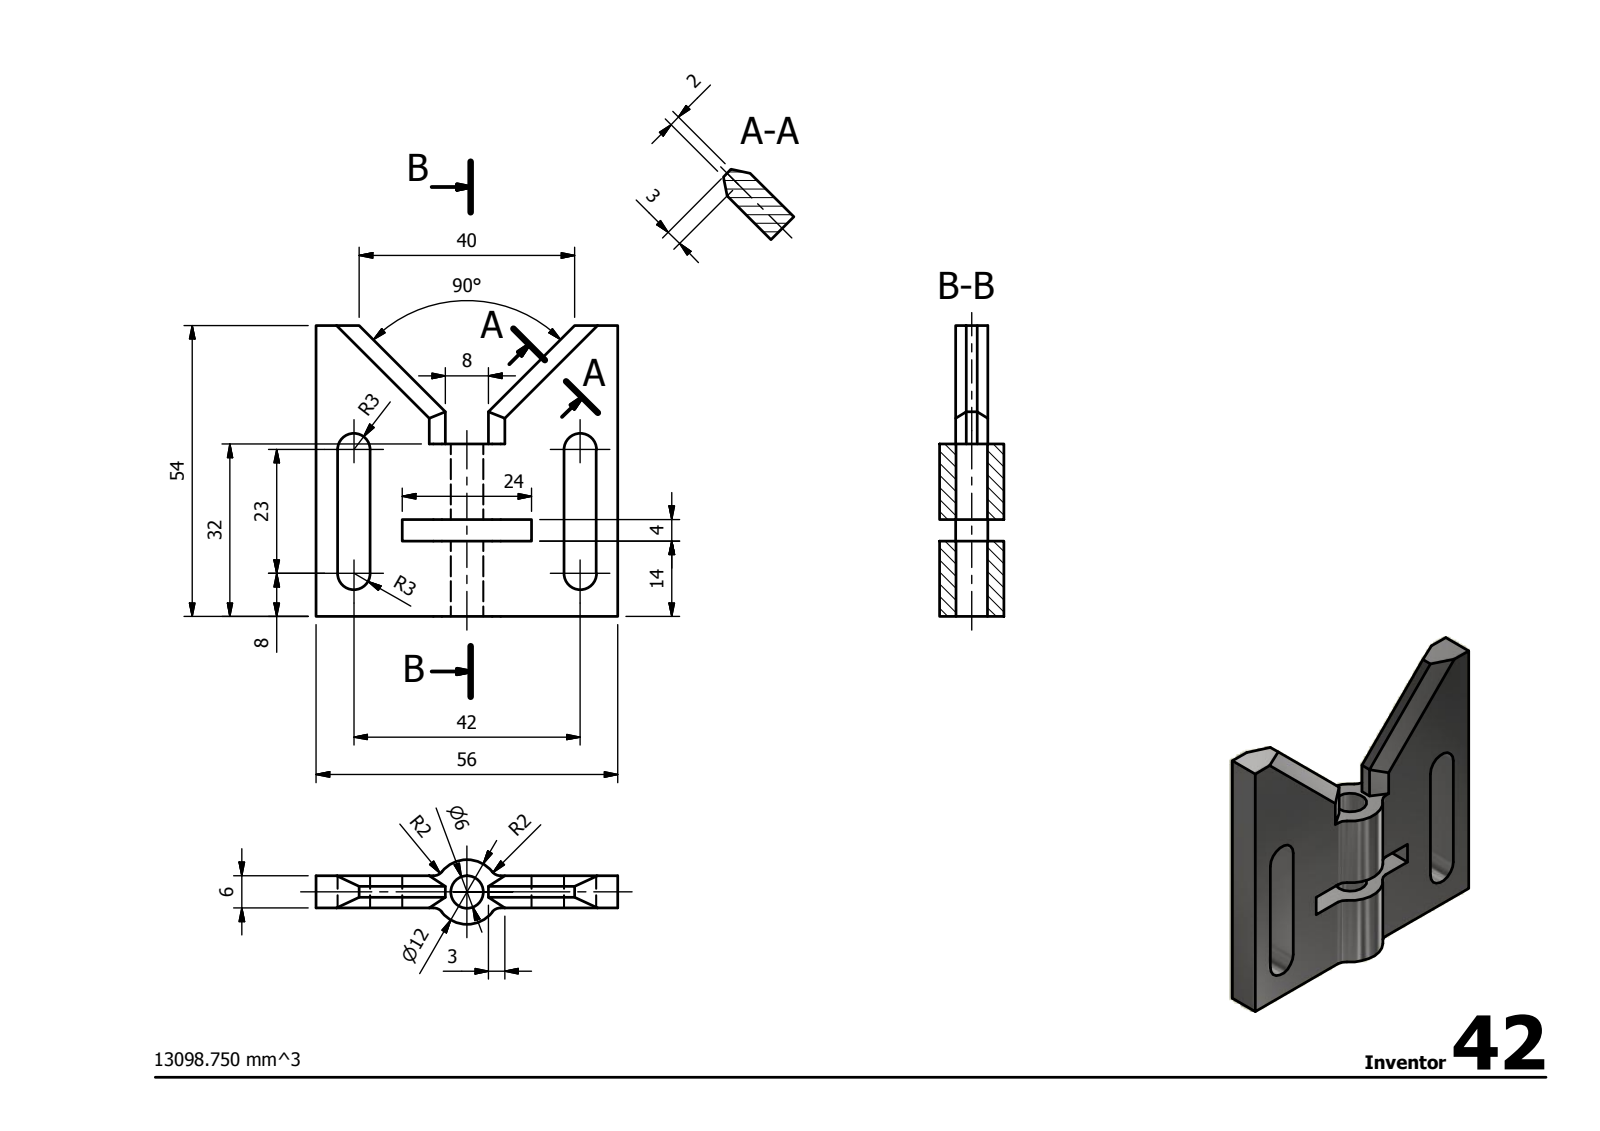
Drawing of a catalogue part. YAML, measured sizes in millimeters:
step_written_by: "Autodesk Inventor 2014 (AUTOMOTIVE_DESIGN)"
units: millimeters
bodies: {solids: 1, faces: 48, planar: 30, cylindrical: 18, other: 0}
overall_size: [56, 54, 12]
volume: 13099
surface_area: 7446
round_holes:
  - {diameter: 6, count: 1}
partial_cylinders:
  - {radius: 2, count: 4}
  - {radius: 3, count: 4}
  - {radius: 6, count: 1}
face_to_face_distances: [6, 4, 56, 10, 46, 52, 42, 36, 14, 18]
